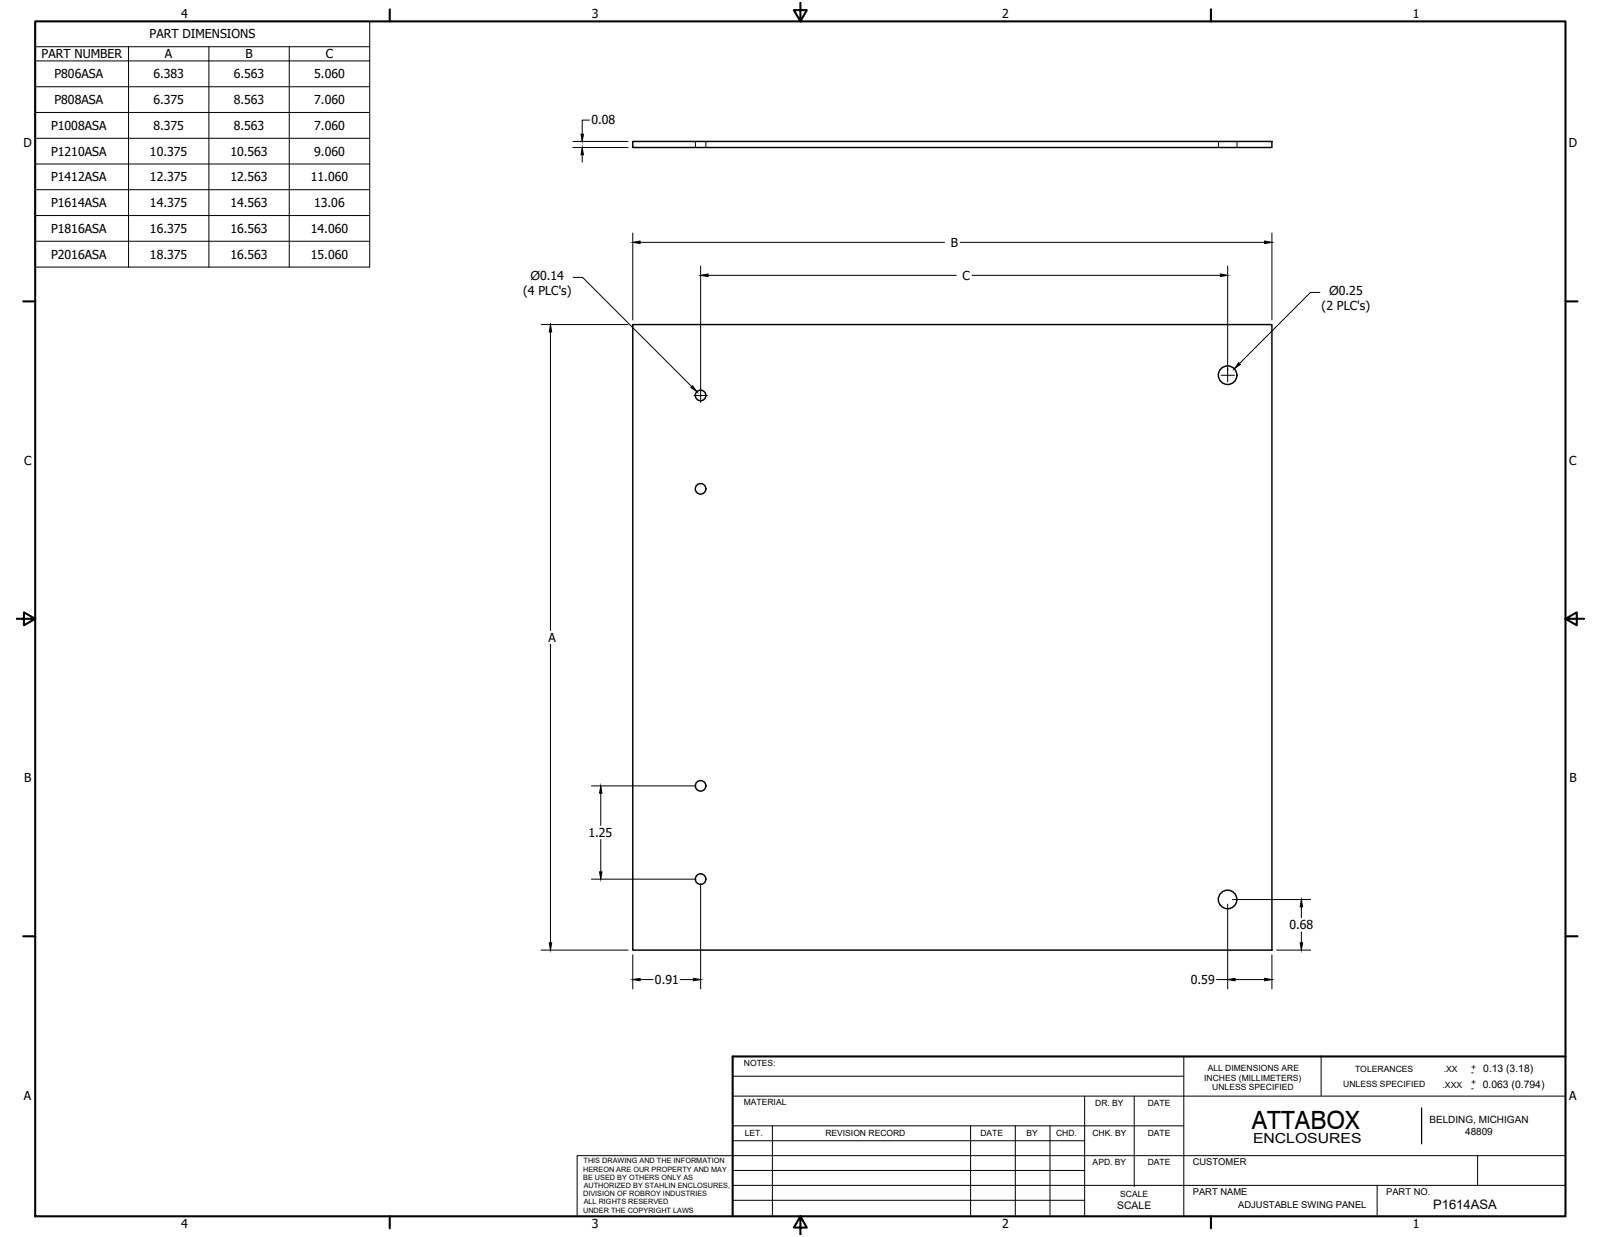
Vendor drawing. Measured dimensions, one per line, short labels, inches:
name: P1614ASAL
written by: Autodesk Inventor 11 (AUTOMOTIVE_DESIGN)
unit: in
bodies: 1 solid, 12 faces (6 planar, 6 cylindrical, 0 other)
size: 14.563 × 14.375 × 0.08
volume: 16.73 in³; area: 423.2 in²
holes: 4× ⌀0.14, 2× ⌀0.25
face distances: 0.08, 14.375, 14.562
hole spacings: 1.25, 11.226, 13.063, 13.148, 17.4, 18.25, 9.976, 12.476
